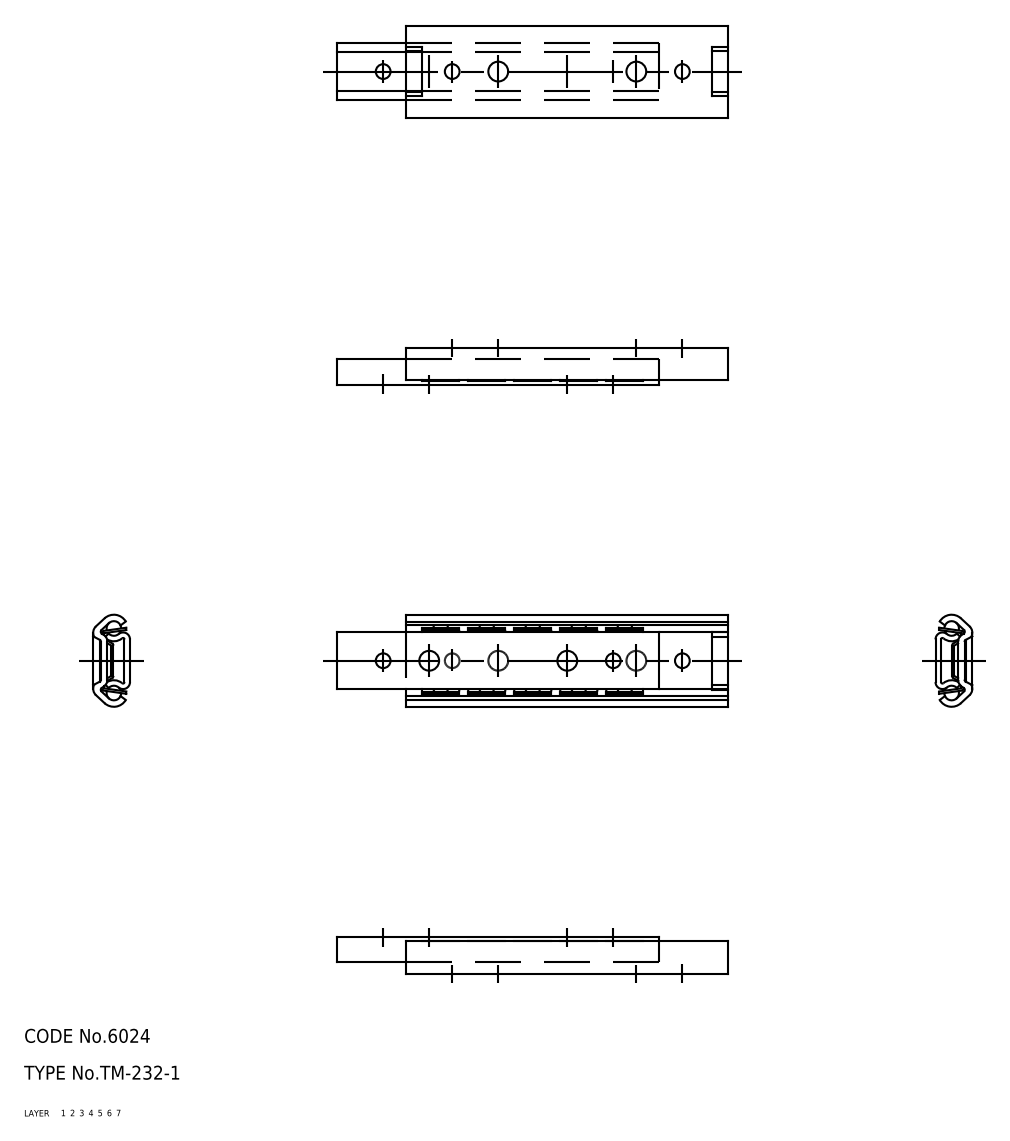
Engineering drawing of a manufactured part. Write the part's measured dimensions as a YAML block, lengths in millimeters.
part_name: "ball; retainer; member_B; member_A (+1 more)"
step_written_by: "CADfix (AUTOMOTIVE_DESIGN)"
units: millimeters
bodies: {solids: 13, faces: 200, planar: 0, cylindrical: 0, other: 200}
overall_size: [85, 20, 8]
volume: 4900
surface_area: 9687
